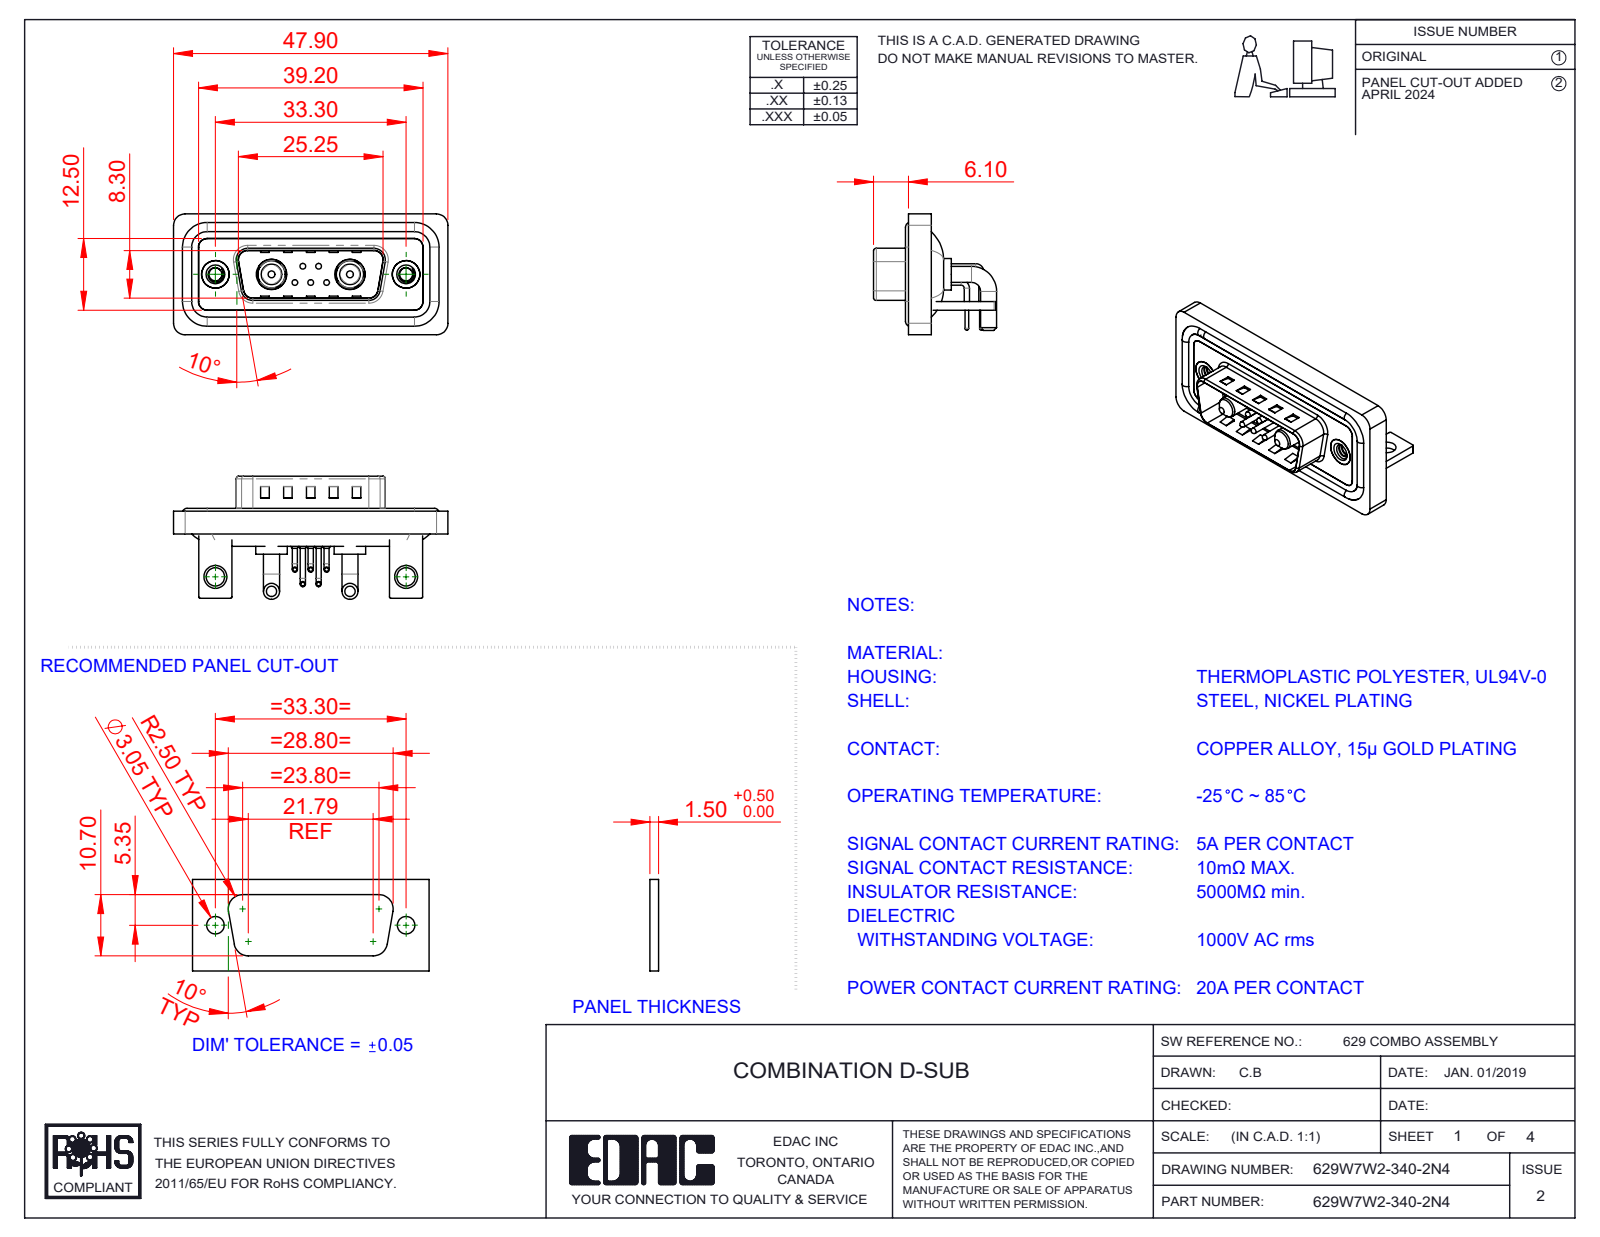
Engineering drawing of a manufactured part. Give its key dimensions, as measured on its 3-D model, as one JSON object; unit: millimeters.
{"part_name": "629W7W2-340-2N4; 629Combo Shell Front_15 Contacts; Power Pin_20A RA; 629Combo Contact Row 1 (+6 more)", "step_written_by": "SolidWorks 2023 (CONFIG_CONTROL_DESIGN)", "units": "millimeters", "bodies": {"solids": 18, "faces": 1123, "planar": 537, "cylindrical": 424, "other": 162}, "overall_size": [47.9, 21.5, 21.1], "volume_mm3": 5958, "surface_area_mm2": 9727, "round_holes": [[0.75, 5], [1.6, 5], [2, 5], [2.26, 2], [3.2, 2], [4, 2], [4.8, 2], [4.85, 2], [5, 2], [5.3, 2]], "round_bosses_or_shafts": [[0.9, 10], [1.5, 5], [1, 5], [0.65, 5], [2.8, 4], [1.6, 4], [5.5, 2], [5.2, 2]], "partial_cylinders_radius": [[2, 21], [1.5, 18], [0.25, 16], [0.5, 9], [1.6, 8], [1.01, 5], [0.6, 4], [0.65, 4]], "face_to_face_distances": [0.4, 1.5, 0.8, 2.9, 2.1, 1.1, 1.6, 1.2, 3.7, 4.5], "hole_center_spacings": [3.16, 2.77, 9.8, 23.5, 33.3, 4.31, 4.33, 5.03]}
